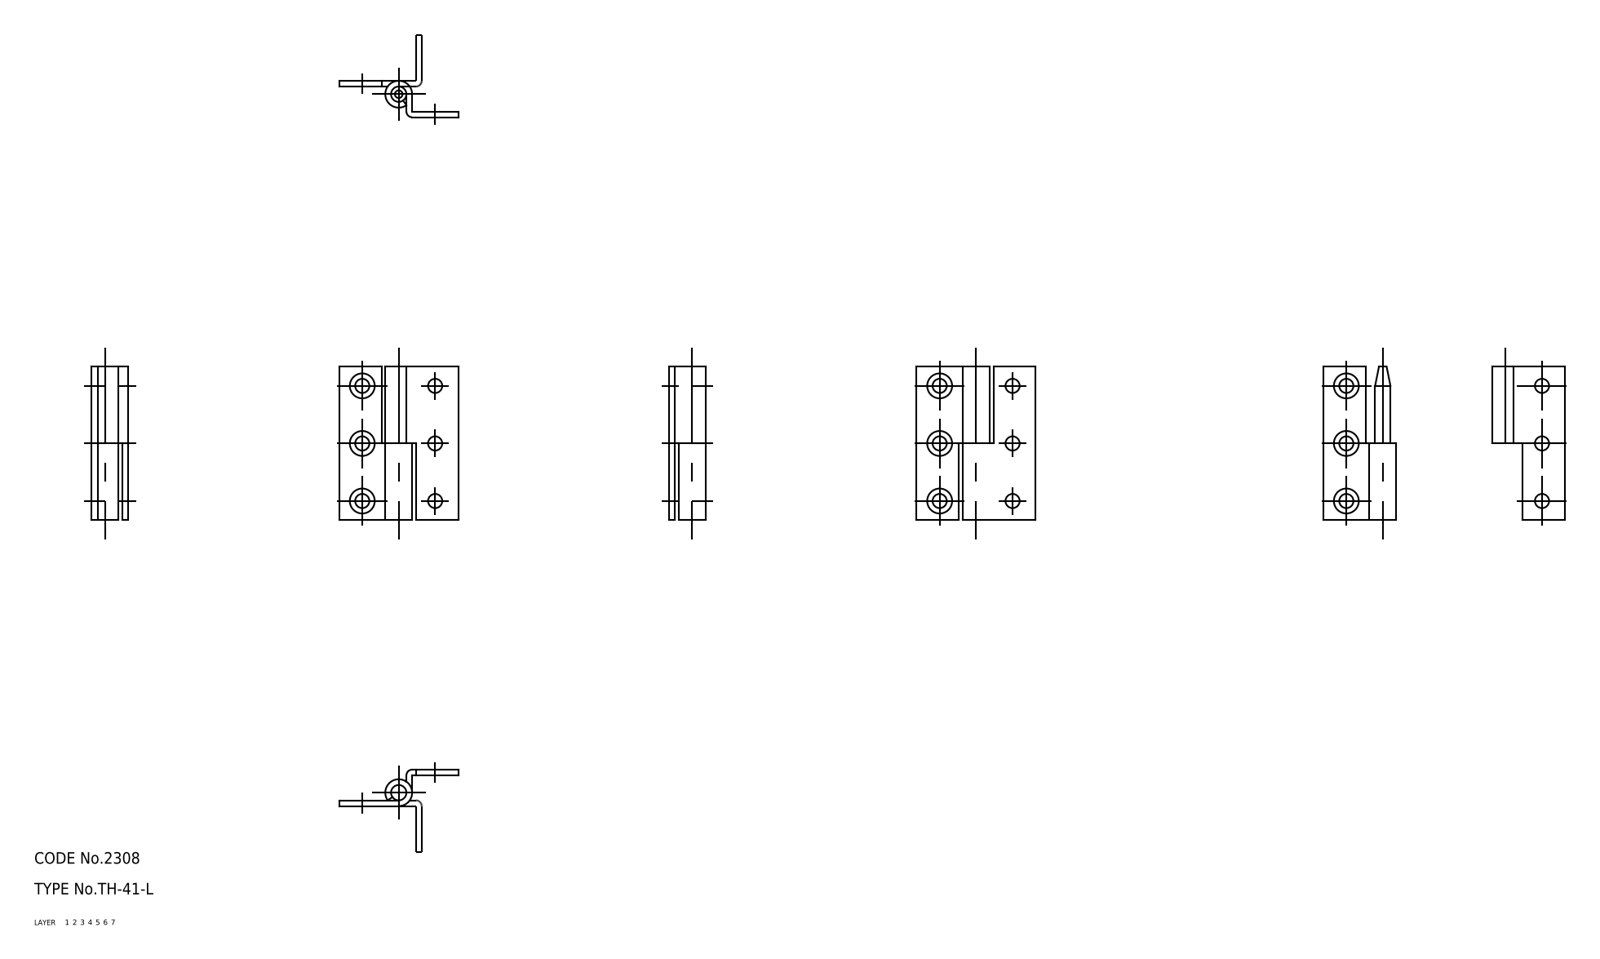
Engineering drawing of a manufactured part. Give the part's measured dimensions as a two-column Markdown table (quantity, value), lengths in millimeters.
| quantity | value |
| --- | --- |
| part name | shaft; hinge piece_B; hinge piece_A; TH_41_L_8820_36 |
| STEP written by | CADfix (AUTOMOTIVE_DESIGN) |
| units | millimeters |
| bodies | 3 solids, 53 faces (0 planar, 0 cylindrical, 53 other) |
| overall size | 40 × 31 × 9.5 |
| volume | 2 825 mm³ |
| surface area | 4 238 mm² |
